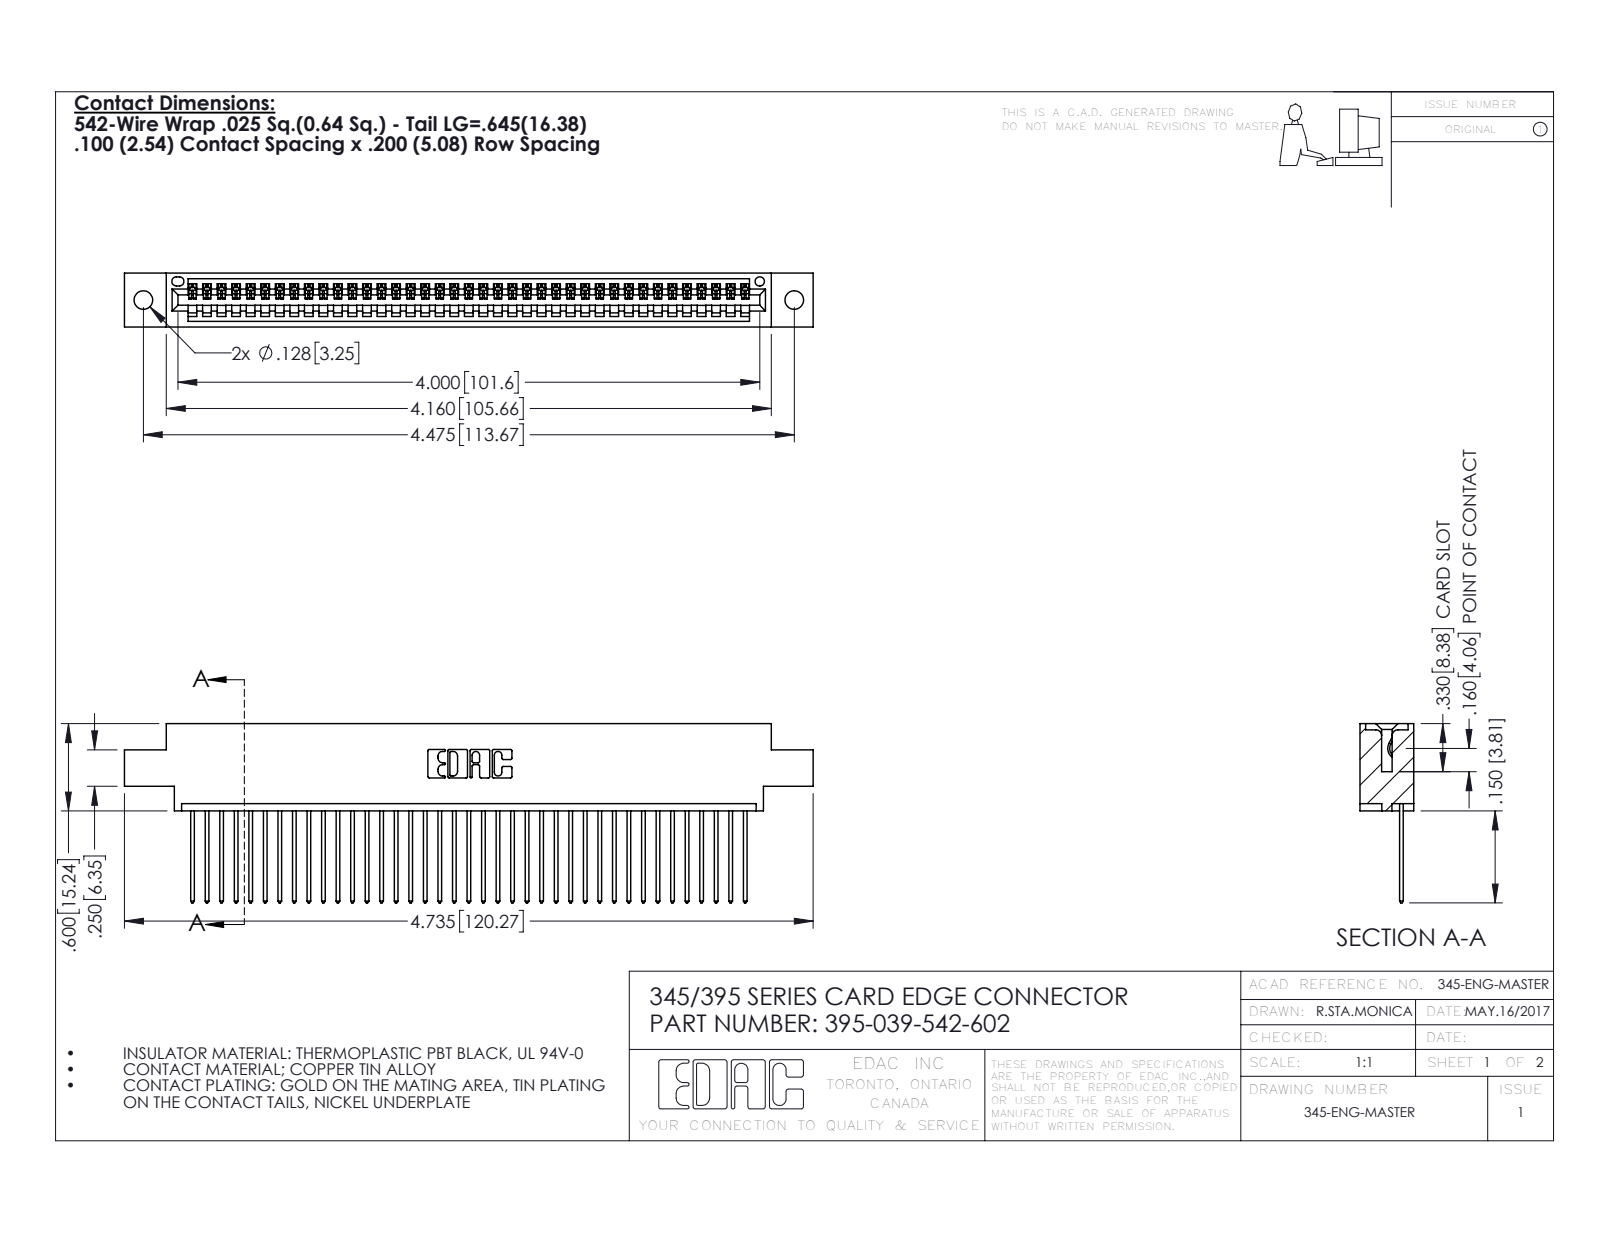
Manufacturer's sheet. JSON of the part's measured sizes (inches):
{"part_name": "345-292-001_345-293-142; 345 Part_0.170 Offset - 0.128 Dia; 395-039-542-602", "step_written_by": "SolidWorks 2016 (CONFIG_CONTROL_DESIGN)", "units": "inches", "bodies": {"solids": 40, "faces": 2392, "planar": 1644, "cylindrical": 748, "other": 0}, "overall_size": [4.735, 1.232, 0.37], "volume_in3": 0.692, "surface_area_in2": 23.91, "round_holes": [[0.128, 2], [0.064, 1]], "partial_cylinders_radius": [[0.006, 78], [0.01, 78], [0.01, 22], [0.007, 6], [0.031, 6], [0.026, 3], [0.031, 2], [0.04, 2]], "face_to_face_distances": [0.072, 0.298, 0.37, 0.098, 0.272, 0.025, 0.2, 0.225, 0.175, 0.149], "hole_center_spacings": [0.27, 4.239, 4.475]}
